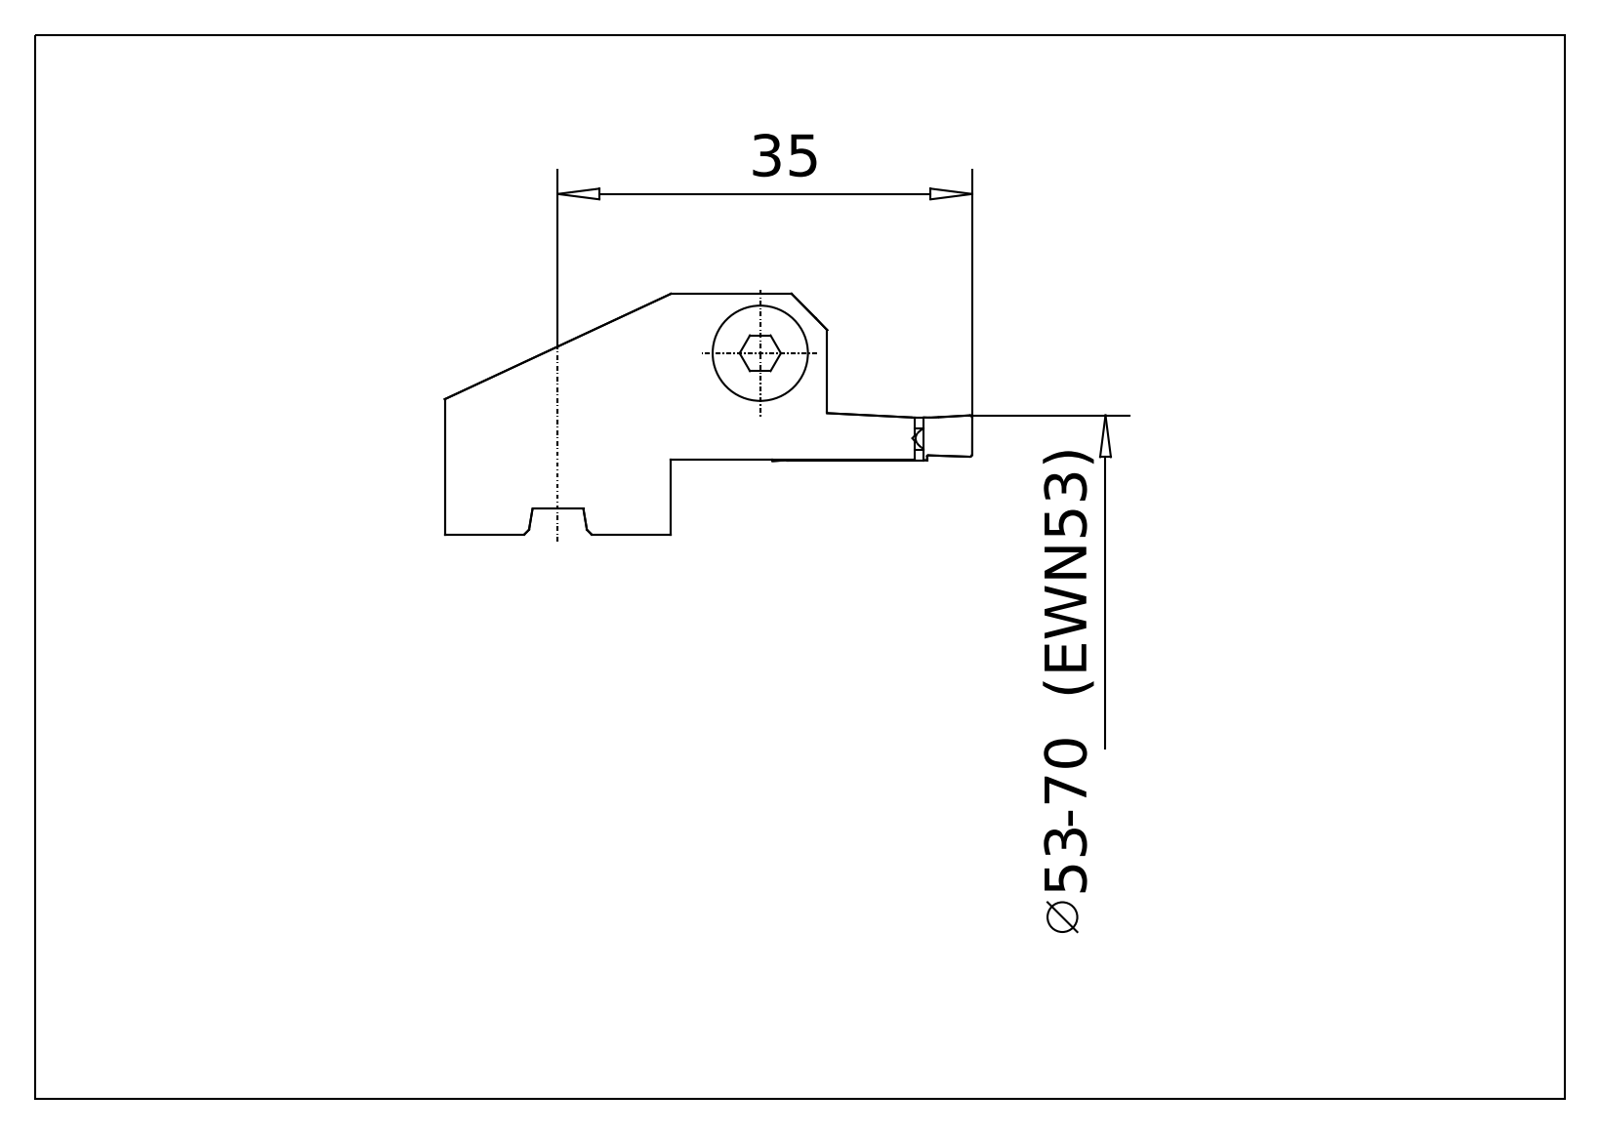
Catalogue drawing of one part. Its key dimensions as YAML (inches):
part_name: "626.935 Kaiser ENH 51 S4 53-70|958.425 Kaiser NP 4250 P20C_Einstechplatte 4mm;NONE; 626.935 Kaiser ENH 51 S4 53-70|690.183 Kaiser Zyl-Schraube M5x12A_Standard;NONE; 626.935 Kaiser ENH 51 S4 53-70|626.935 Kaiser ENH 51 S4 53-70_Standard;NONE"
step_written_by: "ACIS (automotive_design)"
units: inches
bodies: {solids: 3, faces: 131, planar: 78, cylindrical: 38, other: 15}
overall_size: [1.756, 0.793, 0.756]
volume: 0.4
surface_area: 6.49
round_holes:
  - {diameter: 0.354, count: 2}
  - {diameter: 0.165, count: 1}
  - {diameter: 0.199, count: 1}
  - {diameter: 0.209, count: 1}
round_bosses_or_shafts:
  - {diameter: 0.748, count: 1}
  - {diameter: 0.335, count: 1}
  - {diameter: 0.197, count: 1}
partial_cylinders:
  - {radius: 0.008, count: 4}
  - {radius: 0.004, count: 2}
  - {radius: 0.024, count: 2}
  - {radius: 0.049, count: 2}
  - {radius: 0.064, count: 2}
  - {radius: 0.05, count: 1}
face_to_face_distances: [0.138, 0.53, 0.242, 0.305, 0.063, 0.104, 0.085, 0.167, 0.392, 0.053]
hole_center_spacings: [0.421]
